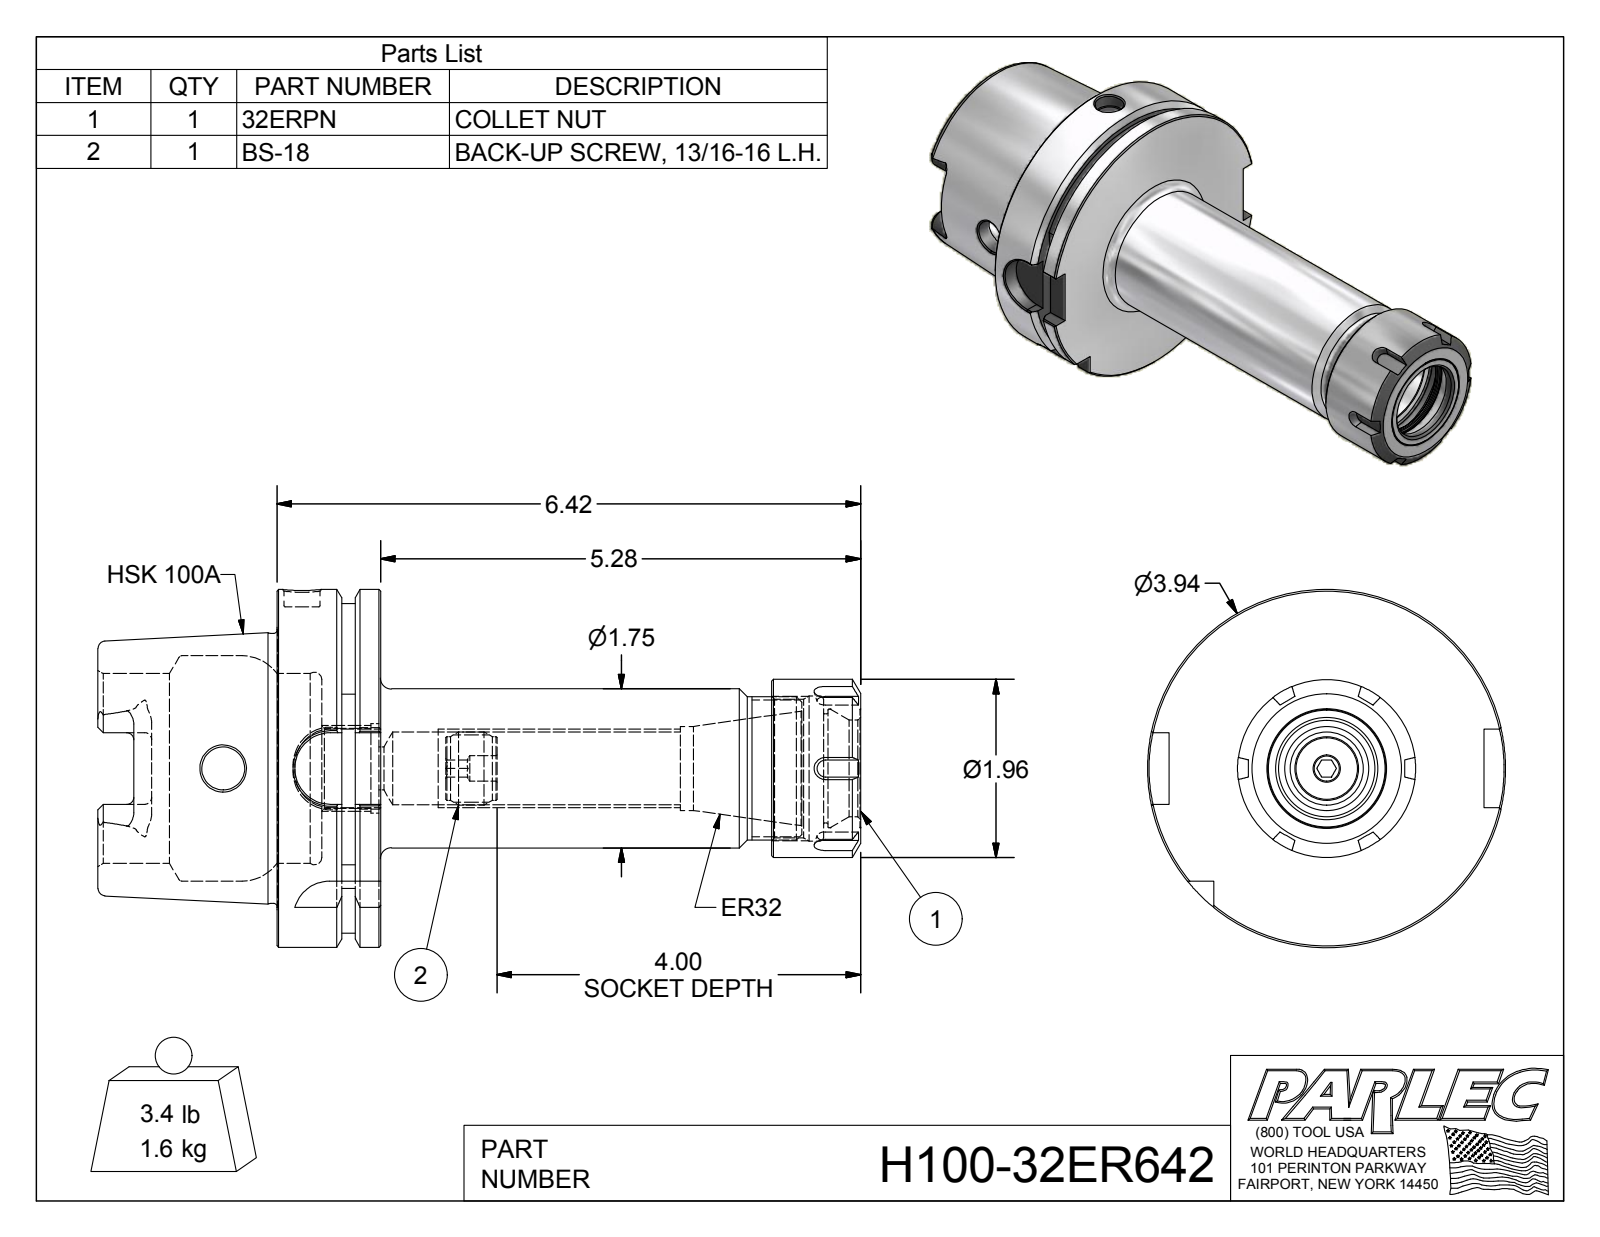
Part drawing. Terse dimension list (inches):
name: H100-32ER642; H100-32ER630; H100-32ER630-1; BS-18 (+1 more)
written by: Autodesk Inventor 2012 (AUTOMOTIVE_DESIGN)
unit: in
bodies: 3 solids, 195 faces (74 planar, 45 cylindrical, 76 other)
size: 8.389 × 3.937 × 3.937
volume: 25.05 in³; area: 130.8 in²
holes: 2× ⌀0.472, 1× ⌀0.28, 1× ⌀0.394, 1× ⌀0.802, 1× ⌀0.881, 1× ⌀0.925, 1× ⌀0.985, 1× ⌀1.063, 1× ⌀1.2, 1× ⌀1.305, 1× ⌀1.523, 1× ⌀1.595
bosses: 1× ⌀3.937, 1× ⌀2.967, 1× ⌀1.958, 1× ⌀1.75, 1× ⌀1.575, 1× ⌀0.805, 1× ⌀0.7
rounds: 6× R0.079, 4× R0.192, 4× R0.394, 1× R1.811
face distances: 1.142, 0.492, 0.65, 1.969, 2.461, 3.11, 8.389, 6.42, 5.928, 5.278
